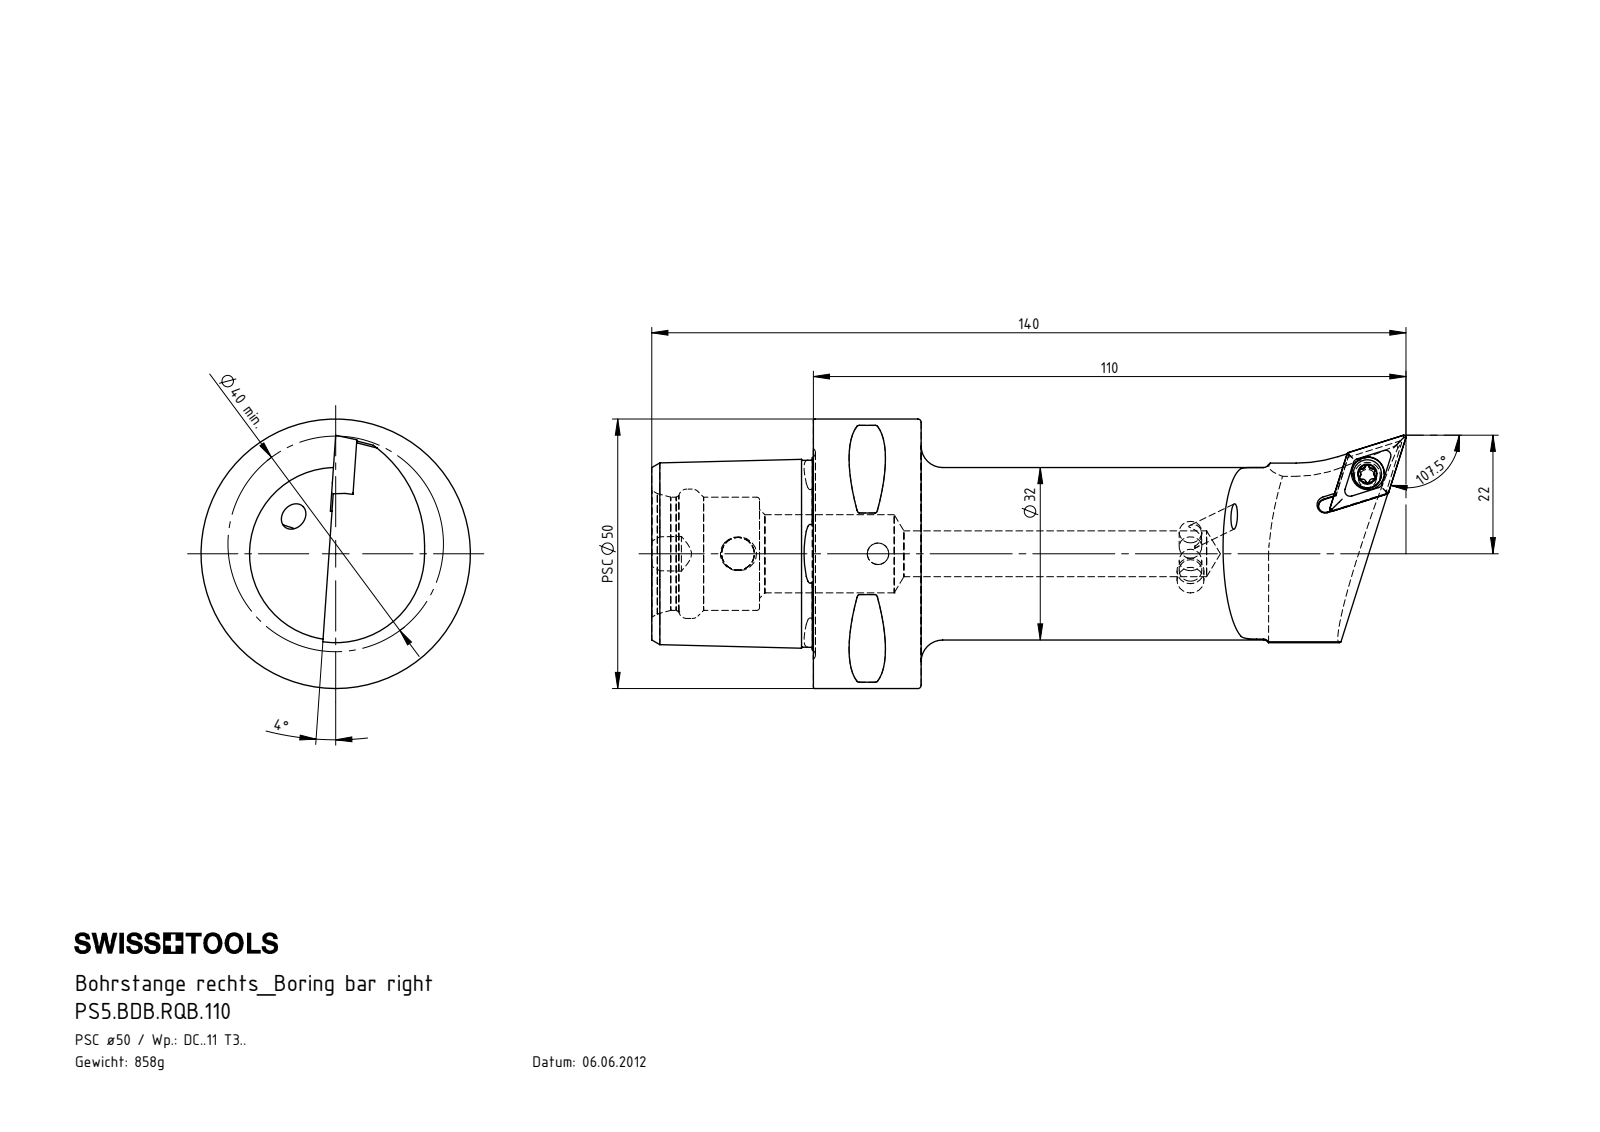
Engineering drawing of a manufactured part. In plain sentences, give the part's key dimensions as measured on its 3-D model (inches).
The part is named "PS5-BDB.RQB.110_A; DCMT11T304; PS5.BDB.RQB.110; KVT_MB_600_050 (+1 more)". Its 3-D file was written by "SolidWorks 2017 (AUTOMOTIVE_DESIGN)". It is 5 solids with 286 faces: 53 planar, 73 cylindrical and 160 other. Overall it measures 5.512 by 1.969 by 1.969 inches. Its volume is 6.653 cubic inches and its surface area 36.62 square inches. Round holes: 2 of diameter 0.157, 2 of diameter 0.165, 2 of diameter 0.24, 1 of diameter 0.13, 1 of diameter 0.173, 1 of diameter 0.335, 1 of diameter 0.571, 1 of diameter 0.827, 1 of diameter 0.945. Round bosses or shafts: 1 of diameter 1.969, 1 of diameter 1.26, 1 of diameter 0.207, 1 of diameter 0.197, 1 of diameter 0.157. Partial cylindrical surfaces (rounded edges, fillets, slot ends): 8 of radius 0.02, 6 of radius 0.013, 6 of radius 0.023, 1 of radius 0.049, 1 of radius 0.118, 1 of radius 0.157, 1 of radius 0.65, 1 of radius 0.906. The main face-to-face distances are 0.787, 1.181, 1.969, 0.755, 0.144, 1.748, 0.394, 1.173, 0.386, 0.795. The hole center spacings are 1.024.
